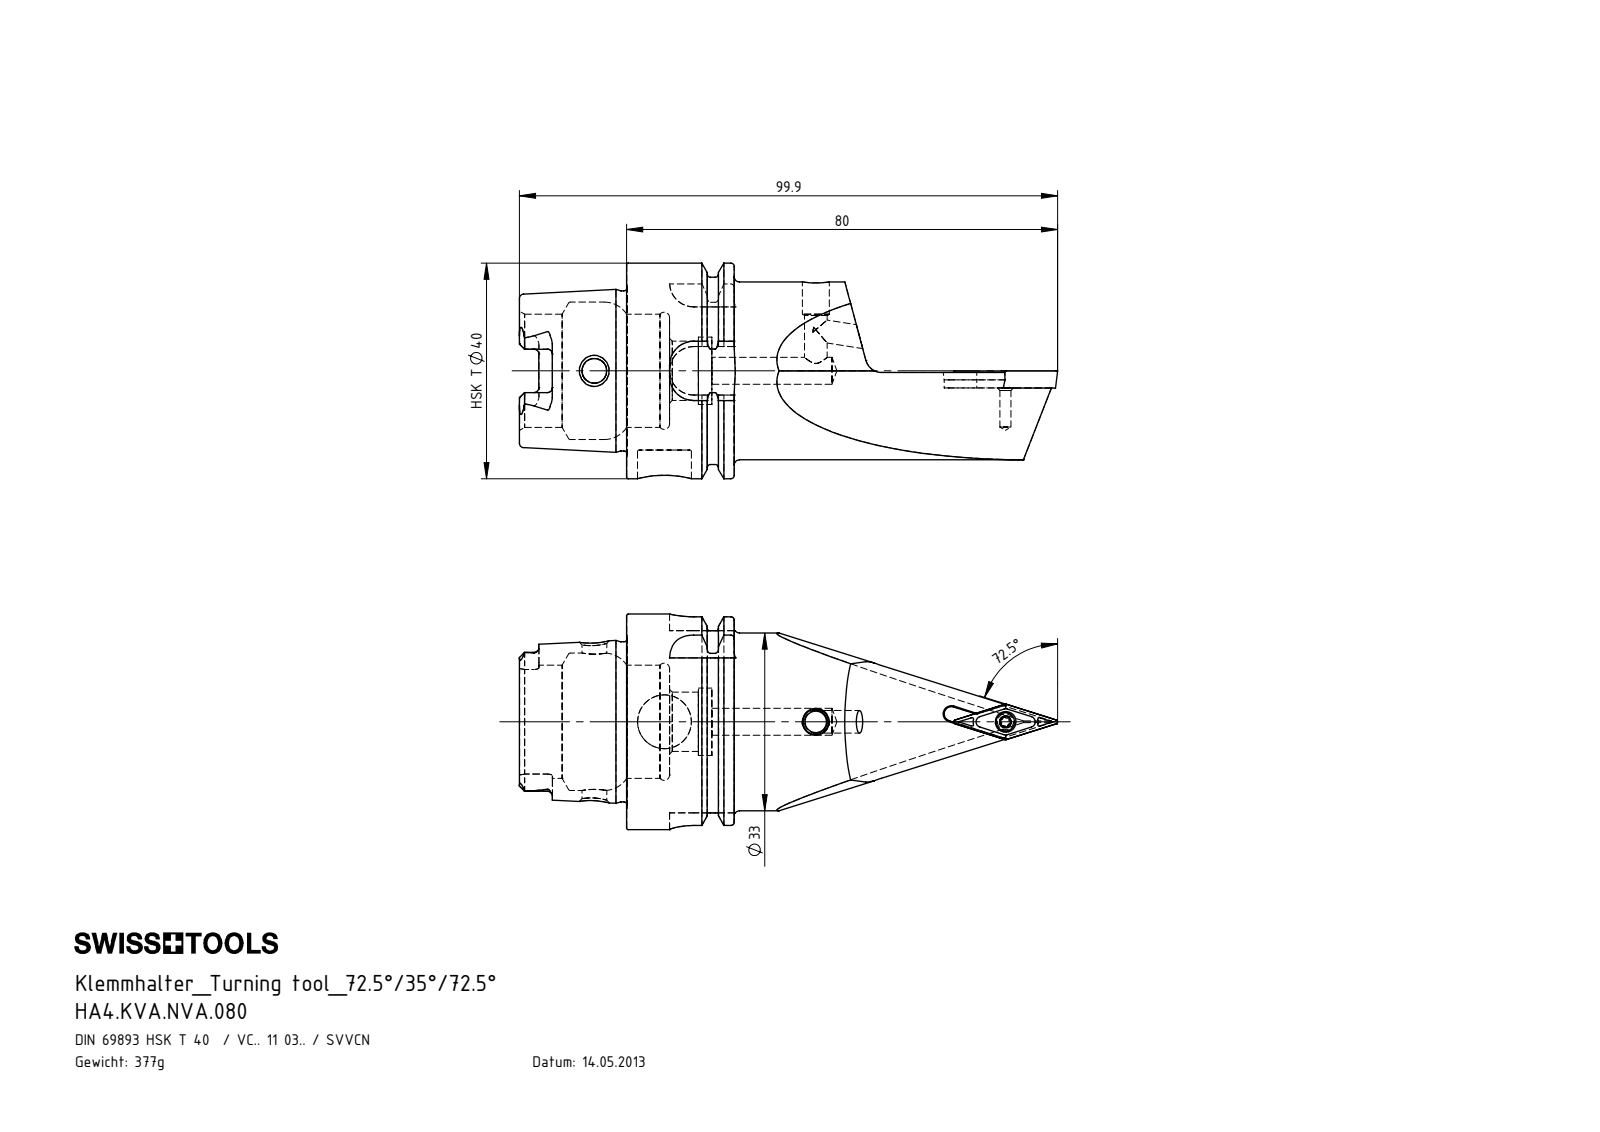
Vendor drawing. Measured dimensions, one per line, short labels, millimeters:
name: WCA-ER2.001.006_A; HA4.KVA.NVA.080; HA4-KVA.NVA.080_A_Fertigbearbeitung; VCGT110304 (+1 more)
written by: SolidWorks 2017 (AUTOMOTIVE_DESIGN)
unit: mm
bodies: 5 solids, 232 faces (81 planar, 59 cylindrical, 92 other)
size: 99.88 × 40 × 40
volume: 47 845 mm³; area: 14 310 mm²
holes: 2× ⌀4.2, 1× ⌀2.05, 1× ⌀2.8, 1× ⌀3.85, 1× ⌀4, 1× ⌀4.6, 1× ⌀5, 1× ⌀10, 1× ⌀11, 1× ⌀12.5, 1× ⌀21, 1× ⌀25.5
bosses: 1× ⌀40, 1× ⌀34.75, 1× ⌀33, 1× ⌀29.71, 1× ⌀5, 1× ⌀3.4, 1× ⌀2.5
rounds: 6× R0.21, 6× R0.9, 5× R0.36, 4× R1.88, 4× R4.5, 1× R0.36, 1× R1.35, 1× R3
face distances: 7.95, 19.95, 12, 19.9, 27.85, 39.85, 2.88, 35.7, 15.8, 7.85
hole spacings: 28.1, 35.19, 35.26, 63.29, 63.36
